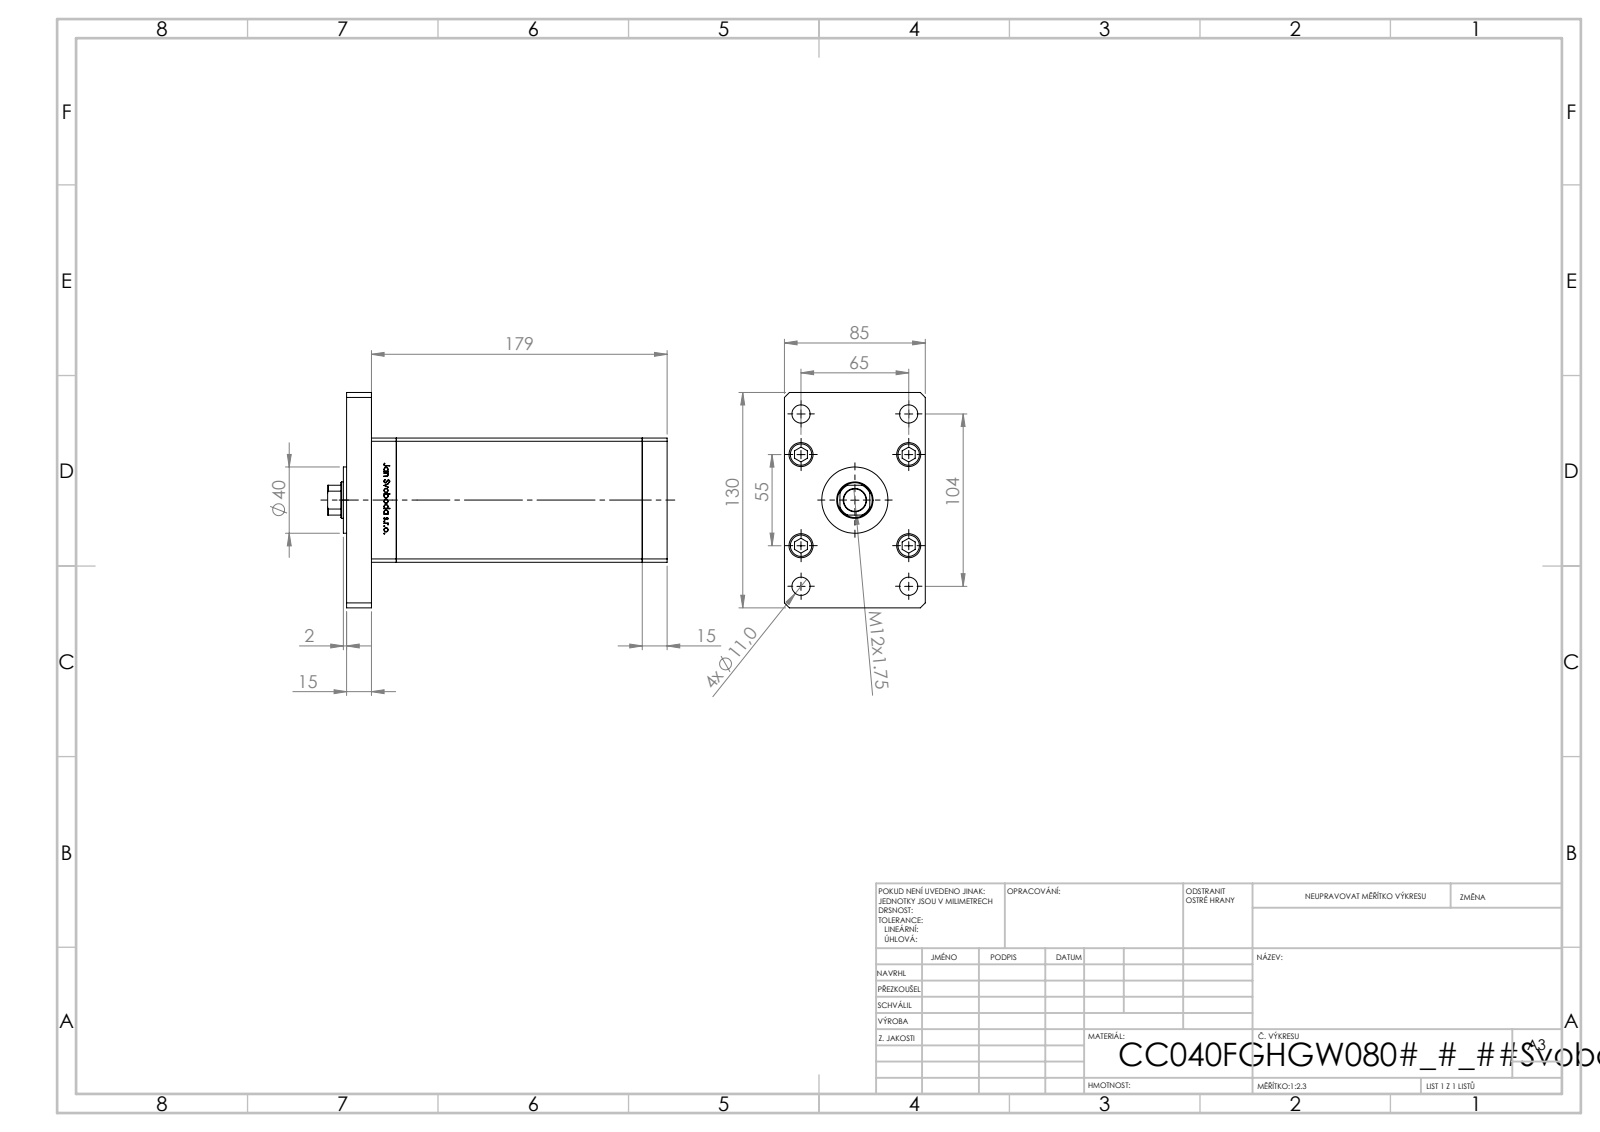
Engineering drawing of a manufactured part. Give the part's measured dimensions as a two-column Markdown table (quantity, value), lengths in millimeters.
| quantity | value |
| --- | --- |
| part name | V220C_F_MIDDLE; V220C BACK_F; ALLEN BOLT; V220C_FRONT_F (+2 more) |
| STEP written by | SolidWorks 2019 (CONFIG_CONTROL_DESIGN) |
| units | millimeters |
| bodies | 19 solids, 1308 faces (515 planar, 187 cylindrical, 606 other) |
| overall size | 205 × 130 × 85 |
| volume | 1 165 000 mm³ |
| surface area | 198 848 mm² |
| round holes (diameter × count) | 11 × 9, 15.5 × 5, 10 × 4, 14.5 × 4, 2 × 2, 13.16 × 2, 13.5 × 1, 22 × 1, 23.5 × 1 |
| round bosses / shafts (diameter × count) | 8 × 9, 14.5 × 5, 40 × 1 |
| partial cylindrical surfaces (radius × count) | 0.93 × 2, 10.5 × 1 |
| main face-to-face distances | 15, 85, 163.5, 178.5, 75, 148.5, 30, 193.5, 10.5, 27.5 |
| hole center spacings | 28, 24.5, 42.57, 61.32, 65, 69.46, 79.5, 102.69 |
